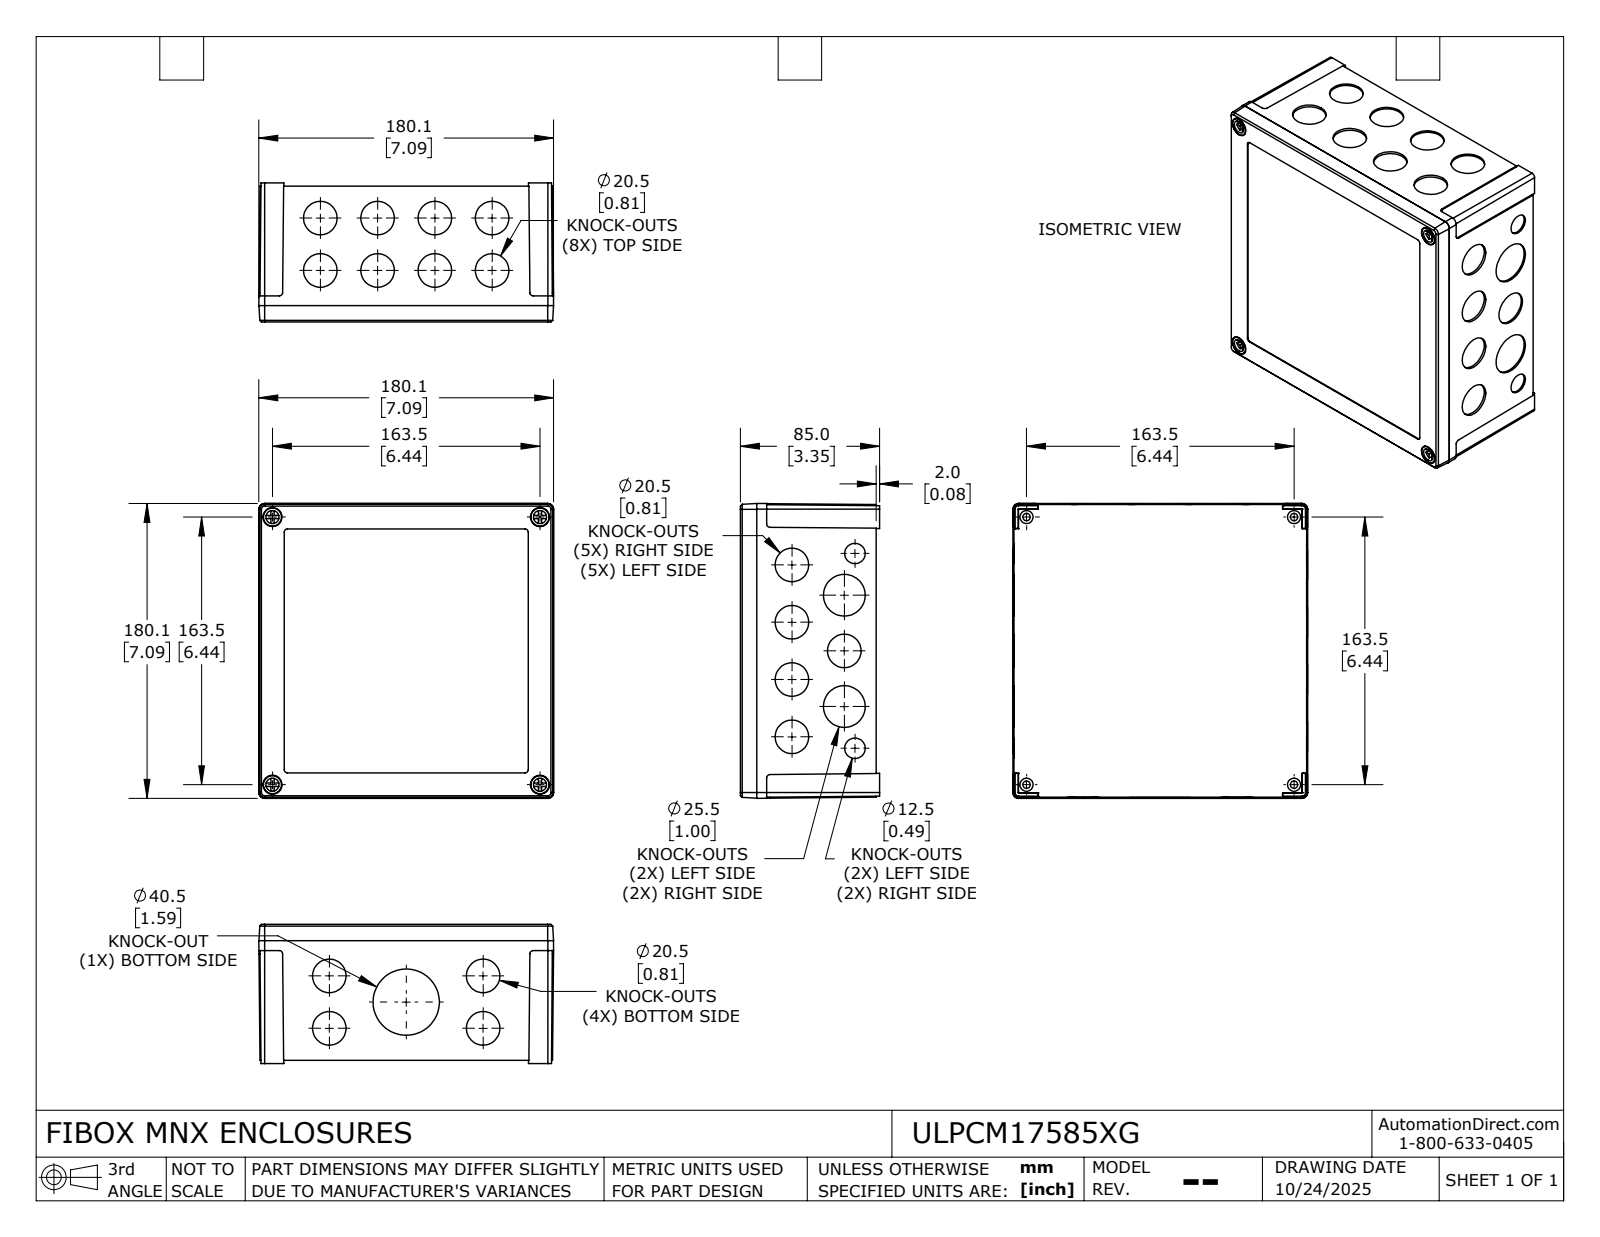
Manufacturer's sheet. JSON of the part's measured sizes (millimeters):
{"part_name": "ULPCM17585XT_Default", "step_written_by": "SolidWorks 2024 (CONFIG_CONTROL_DESIGN)", "units": "millimeters", "bodies": {"solids": 12, "faces": 495, "planar": 323, "cylindrical": 128, "other": 44}, "overall_size": [180.1, 180.1, 85], "volume_mm3": 426151, "surface_area_mm2": 259350, "round_holes": [[20.5, 17], [3.2, 12], [4, 12], [4.5, 4], [8, 4], [11.6, 4], [12.5, 2], [25.5, 2], [40.5, 1]], "round_bosses_or_shafts": [[8, 12], [2.5, 8], [11, 4], [7.2, 4]], "partial_cylinders_radius": [[2, 8], [5, 4]], "face_to_face_distances": [80, 3, 4.2, 77, 2.5, 82.5, 79.5, 83, 0.5, 73], "hole_center_spacings": [35, 33.85, 50, 72.8, 82.59, 121.66, 132.27, 138.92]}
